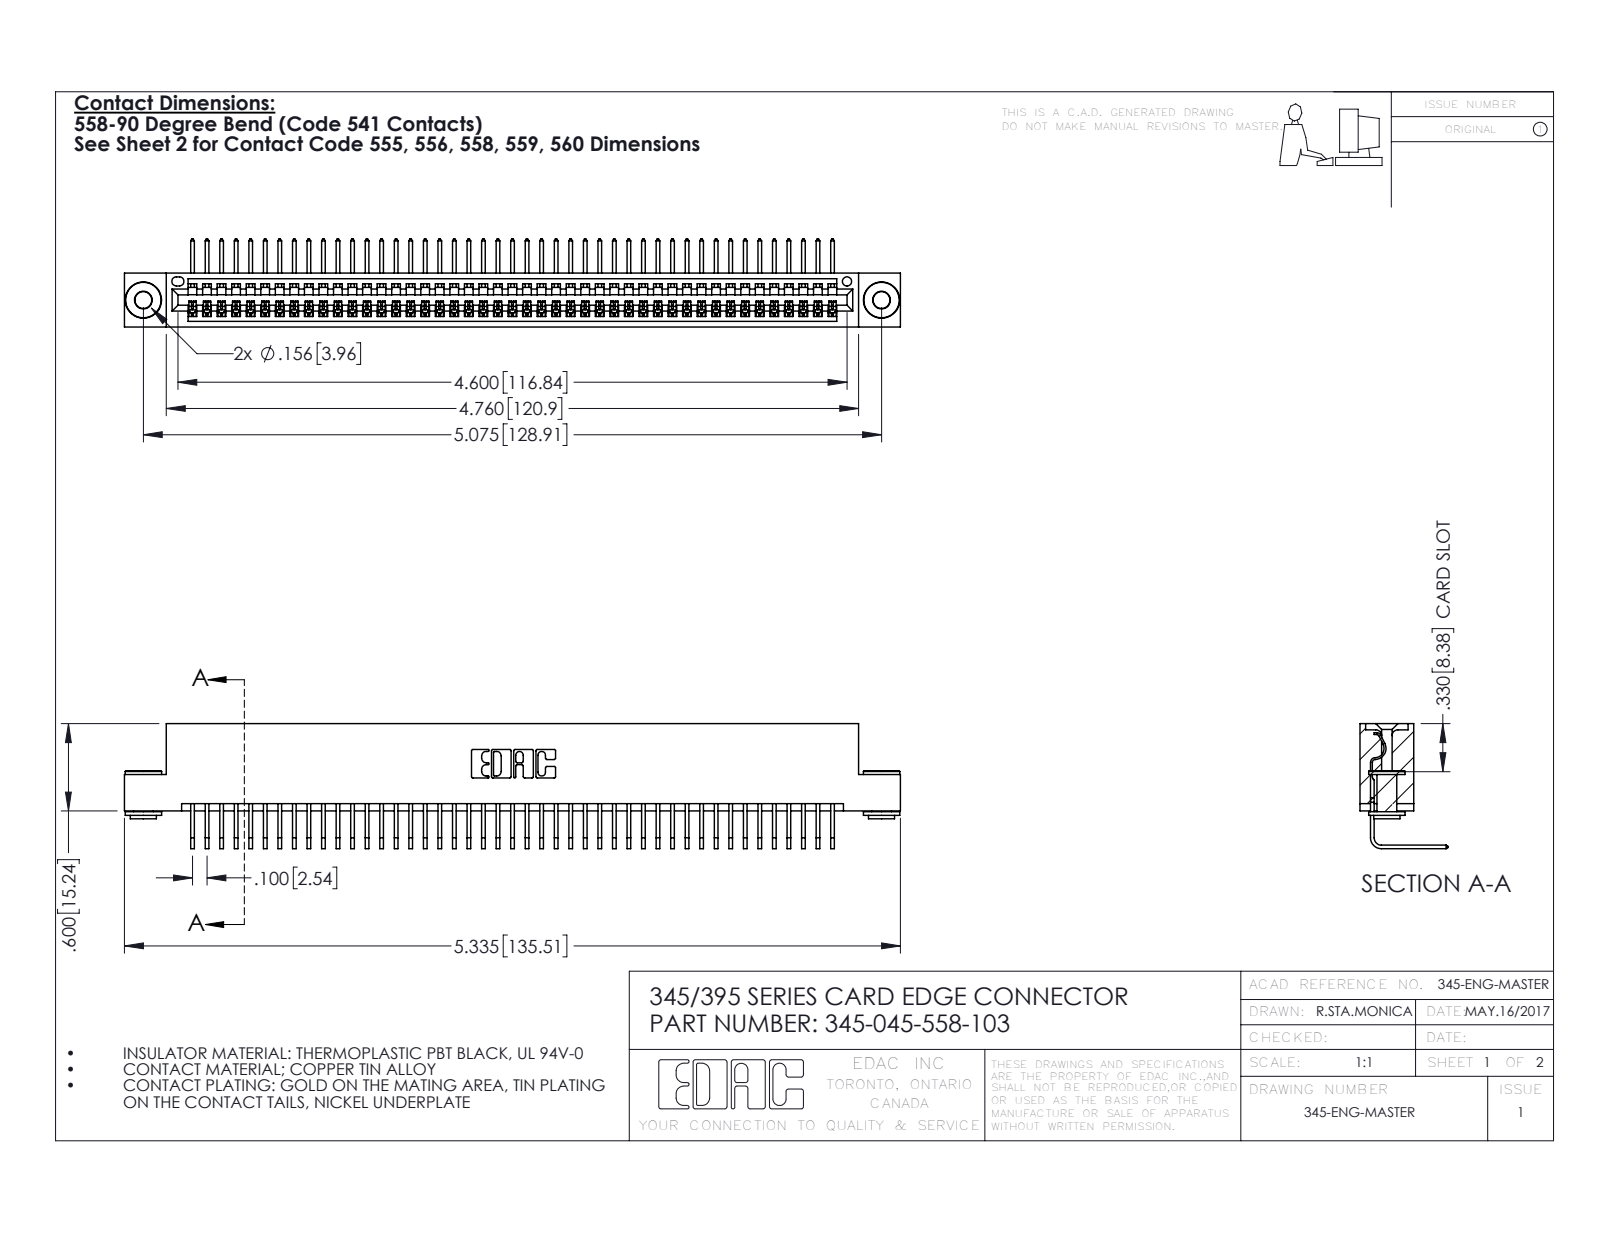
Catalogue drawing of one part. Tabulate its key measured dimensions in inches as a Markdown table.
| quantity | value |
| --- | --- |
| part name | 345-292-001_558 Tail - 2; 345-250-002_345-250-002-102; 345 Part_Flush Mounting Lugs - 0.156 Dia-TH; 345-045-558-103 |
| STEP written by | SolidWorks 2016 (CONFIG_CONTROL_DESIGN) |
| units | inches |
| bodies | 48 solids, 2864 faces (1980 planar, 876 cylindrical, 8 other) |
| overall size | 5.335 × 0.859 × 0.605 |
| volume | 0.797 in³ |
| surface area | 28.67 in² |
| round holes (diameter × count) | 0.116 × 2, 0.156 × 2, 0.064 × 1 |
| round bosses / shafts (diameter × count) | 0.25 × 2, 0.18 × 2, 0.136 × 2 |
| partial cylindrical surfaces (radius × count) | 0.006 × 90, 0.01 × 22, 0.007 × 6, 0.031 × 6, 0.026 × 3, 0.031 × 2, 0.04 × 2, 0.014 × 1 |
| main face-to-face distances | 0.072, 0.298, 0.37, 0.2, 0.025, 0.098, 0.272, 0.225, 0.149, 0.072 |
| hole center spacings | 0.27, 4.839, 5.075 |
